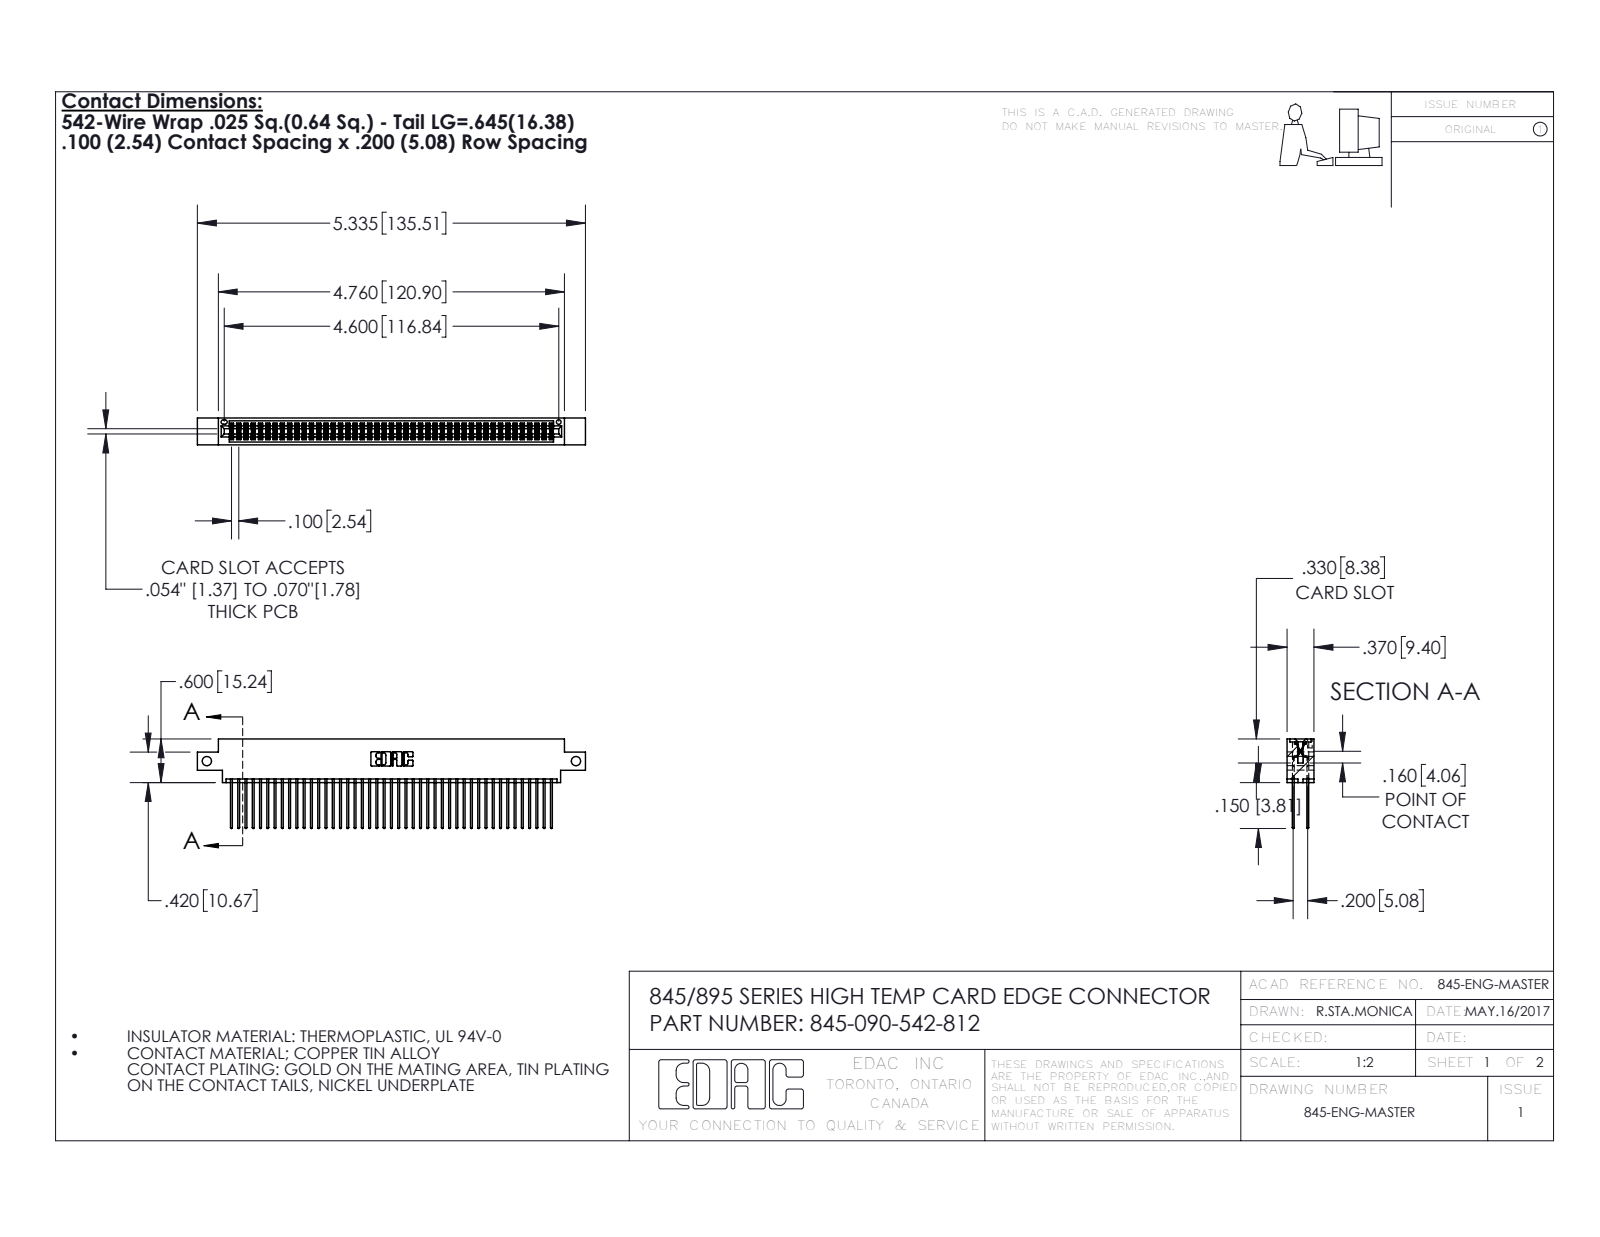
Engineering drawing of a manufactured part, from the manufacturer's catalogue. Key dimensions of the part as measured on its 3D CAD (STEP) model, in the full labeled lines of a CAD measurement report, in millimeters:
Part name (STEP PRODUCT): 345-090-542-812; 345-292-001_345-293-142; 345 Part_0.170 Offset - Side Mount
STEP written by: SolidWorks 2016 (CONFIG_CONTROL_DESIGN)
Units: millimetres
Bodies: 91 solids, 4630 faces (3054 planar, 1576 cylindrical, 0 other)
Overall size (bounding box): 135.5 × 31.3 × 9.4
Volume: 13 400 mm³ · Surface area: 21 850 mm²
Round holes (diameter × count): ⌀3.3 ×2, ⌀1.6 ×1
Partial cylindrical surfaces — rounded edges, fillets, slot ends (radius × count): R0.2 ×135, R0.3 ×90, R0.3 ×22, R0.2 ×6, R0.8 ×6, R0.7 ×3, R0.4 ×2, R0.5 ×2
Main face-to-face distances: 1.8, 7.6, 5.1, 2.5, 6.9, 0.6, 9.4, 5.7, 4.4, 3.8
Hole centre spacings: 128.9
